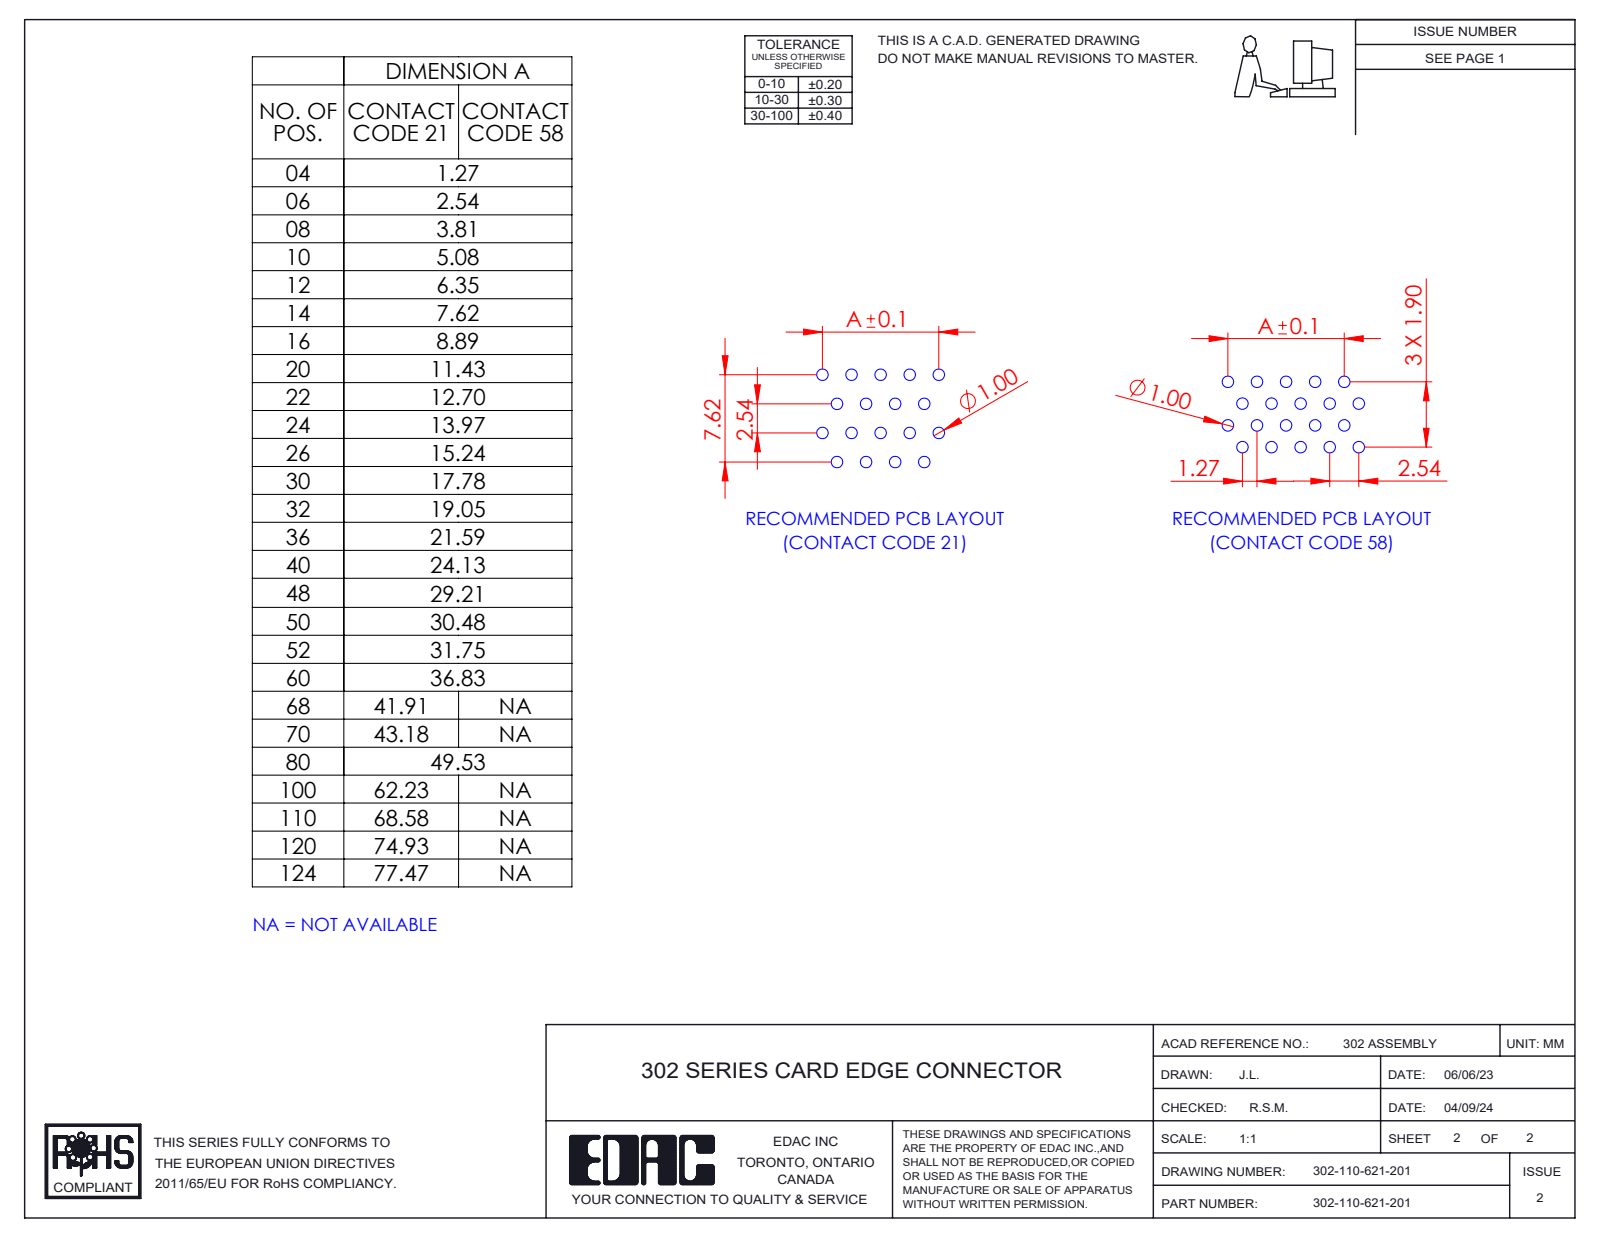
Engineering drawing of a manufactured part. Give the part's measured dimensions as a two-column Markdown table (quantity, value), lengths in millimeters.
| quantity | value |
| --- | --- |
| part name | HSG_Vertical HSG; 302-110-621-201; Contact_302-290-X21 (1); Contact_302-290-X21 (2) |
| STEP written by | SolidWorks 2023 (CONFIG_CONTROL_DESIGN) |
| units | millimeters |
| bodies | 111 solids, 5071 faces (3734 planar, 1113 cylindrical, 224 other) |
| overall size | 75.95 × 17.63 × 8.88 |
| volume | 5 789 mm³ |
| surface area | 16 510 mm² |
| partial cylindrical surfaces (radius × count) | 0.2 × 118, 2.03 × 4, 2.09 × 4, 0.11 × 2, 0.4 × 2, 0.41 × 2, 1.25 × 2, 1.53 × 2 |
| main face-to-face distances | 2.54, 8.88, 1.27, 5.08, 3.81, 7.62, 6.35, 8.89, 10.16, 11.43 |
